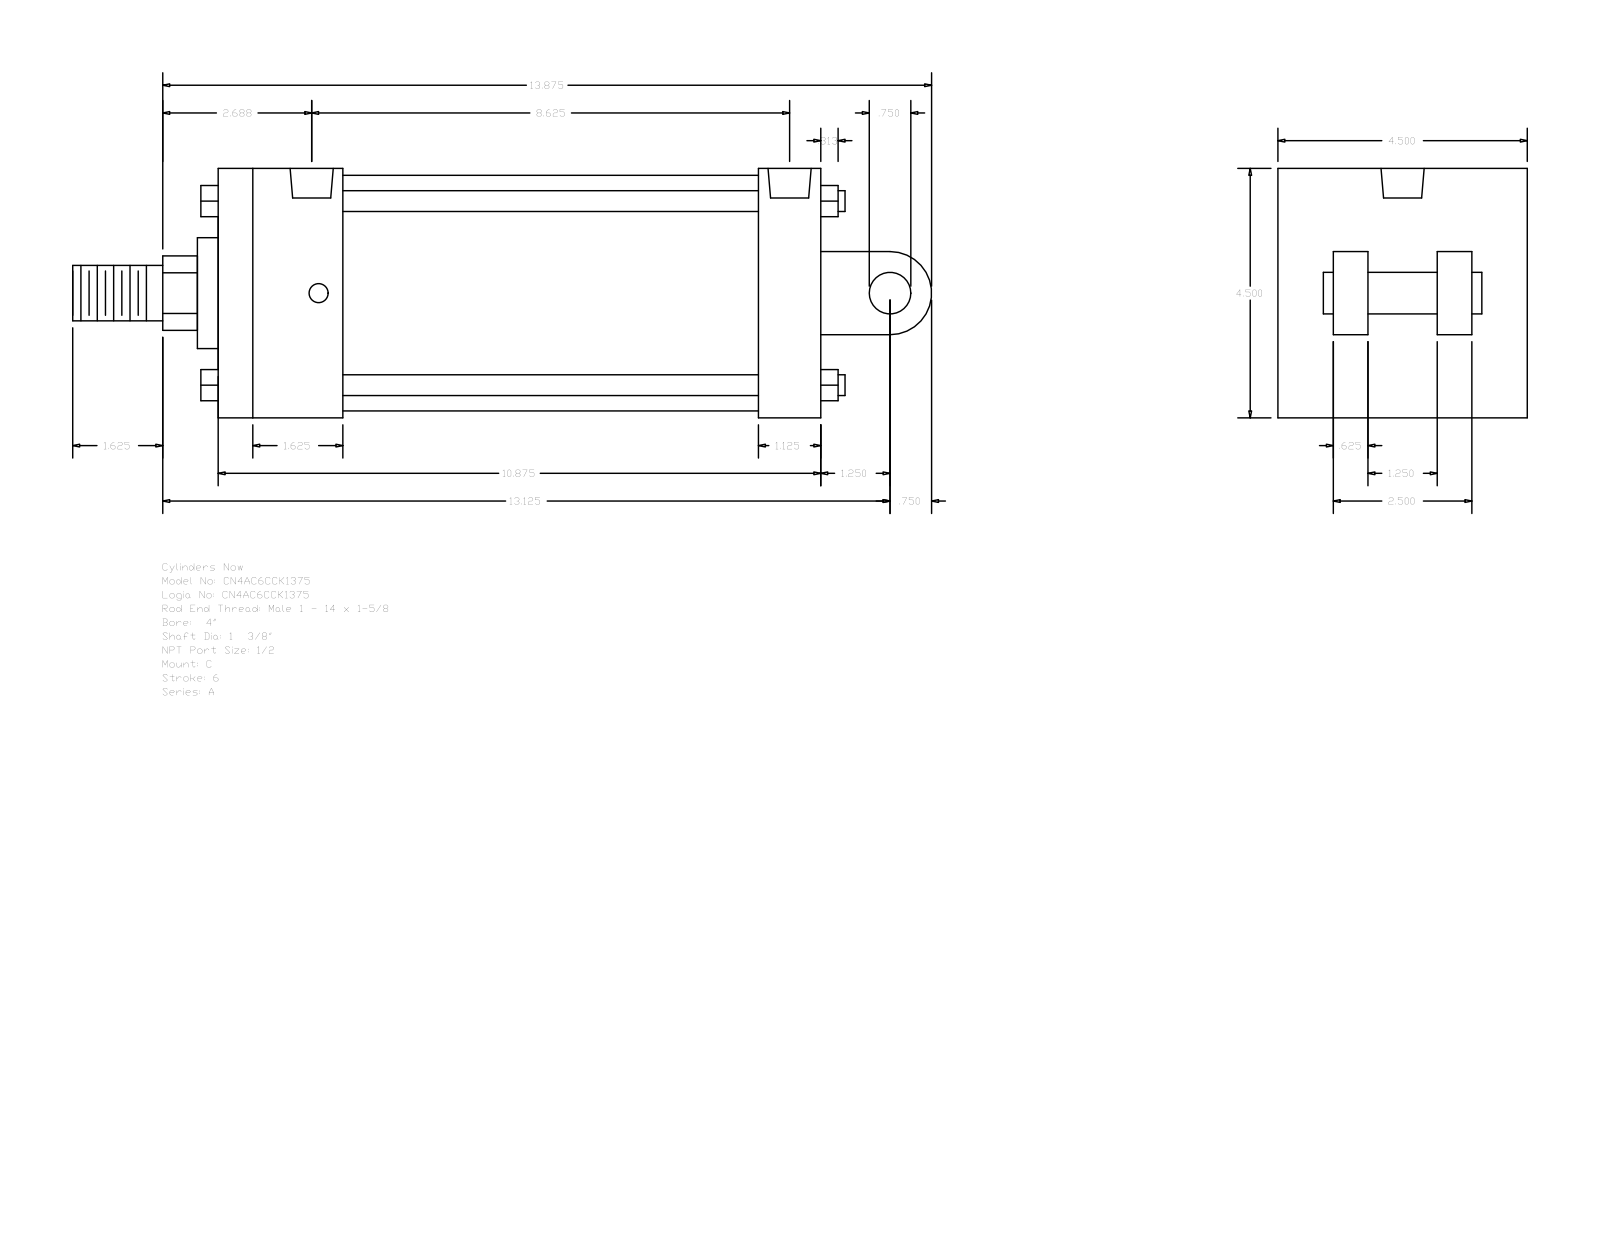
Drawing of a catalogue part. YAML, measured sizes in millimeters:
part_name: "A_C__0400_1.375"
step_written_by: "GSSL Pune (CONFIG_CONTROL_DESIGN)"
units: millimeters
bodies: {solids: 0, faces: 135, planar: 102, cylindrical: 33, other: 0}
overall_size: [393.7, 114.3, 114.3]
round_holes:
  - {diameter: 8.73, count: 4}
  - {diameter: 19.77, count: 2}
round_bosses_or_shafts:
  - {diameter: 9.53, count: 4}
  - {diameter: 107.95, count: 1}
  - {diameter: 50.8, count: 1}
  - {diameter: 34.92, count: 1}
  - {diameter: 25.4, count: 1}
  - {diameter: 19.05, count: 1}
partial_cylinders:
  - {radius: 17.06, count: 1}
  - {radius: 19.05, count: 1}
face_to_face_distances: [114.3, 276.22, 57.15, 73.03, 247.65, 28.57, 190.5, 219.07, 41.27, 25.4]
hole_center_spacings: [3.18, 212.72, 215.9, 219.08]
